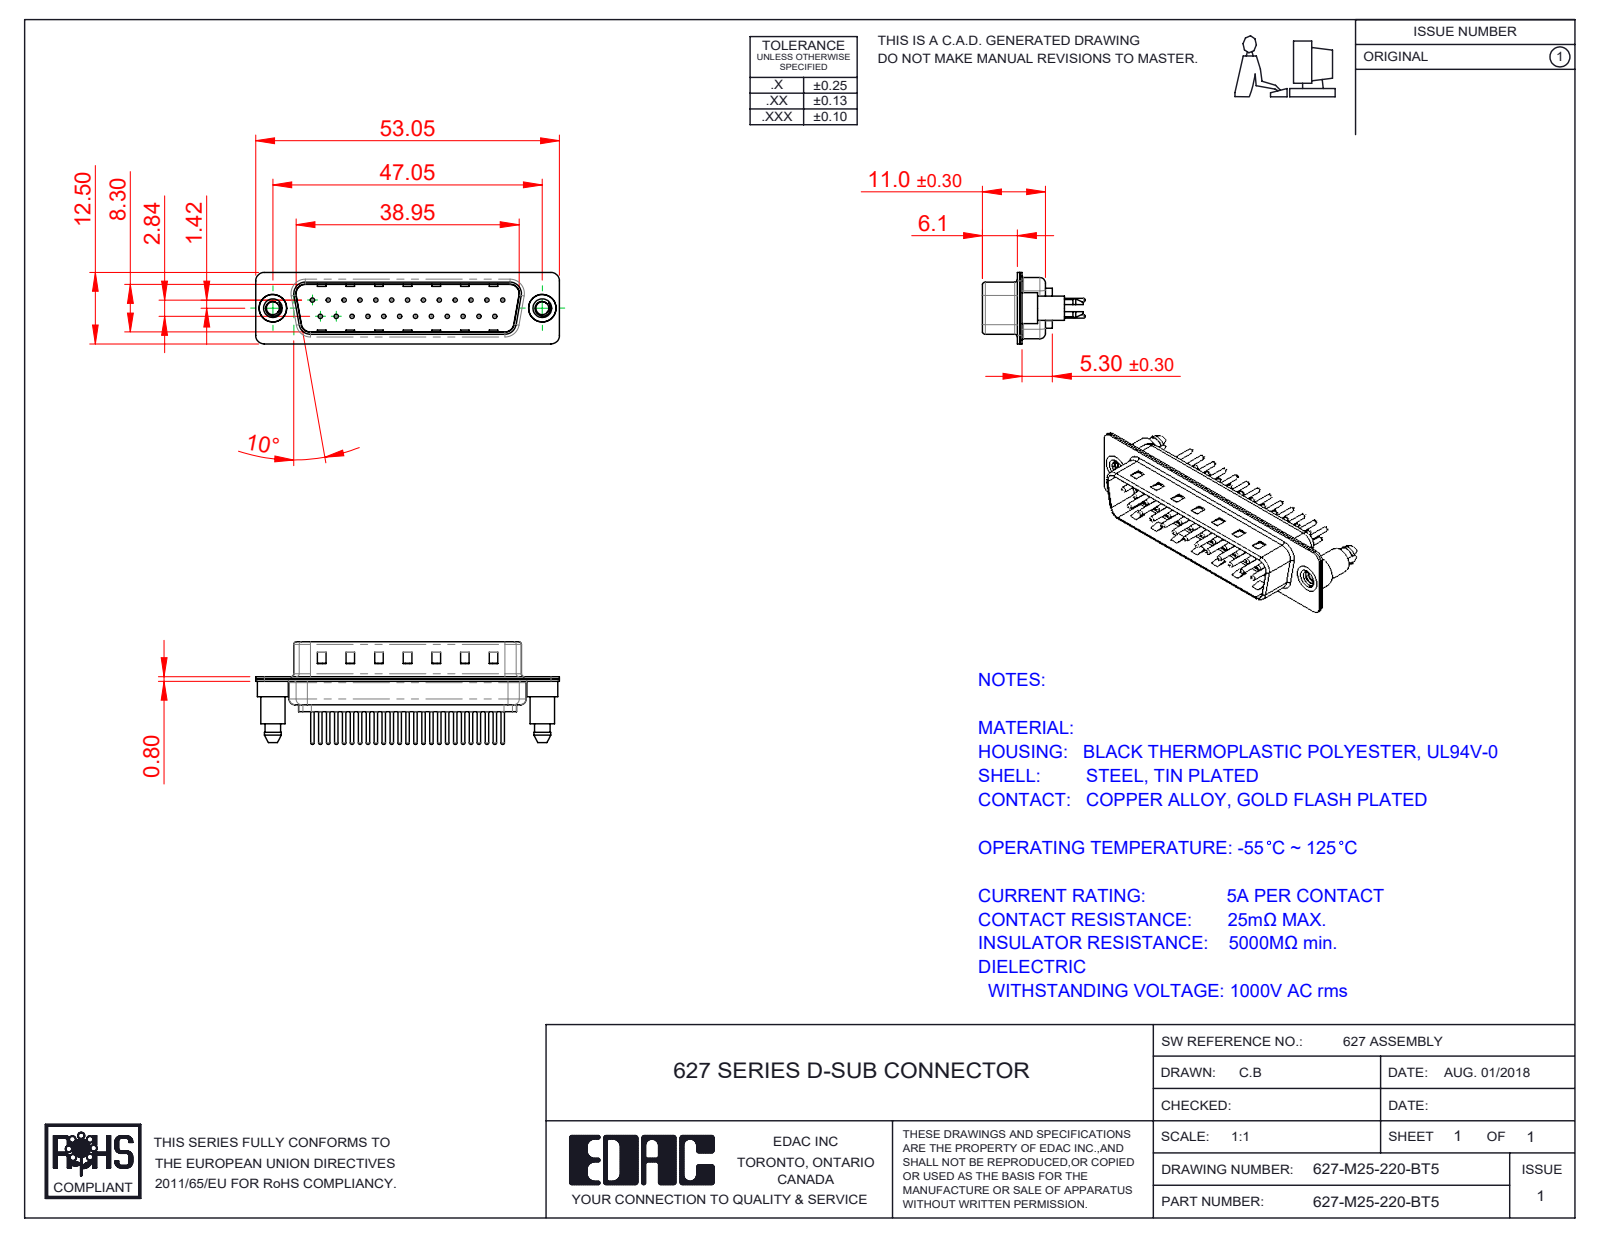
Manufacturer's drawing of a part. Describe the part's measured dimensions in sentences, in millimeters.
The part is named "627M Housing_25 Contacts; 627-M25-220-BT5; 627M Contact Row 2_20; 627M Shell Front_25 Contacts (+3 more)". Its 3-D file was written by "SolidWorks 2020 (CONFIG_CONTROL_DESIGN)". It is 30 solids with 1351 faces: 362 planar, 519 cylindrical and 470 other. Overall it measures 53.05 by 17.9 by 12.5 millimeters. Its volume is 2 853 cubic millimeters and its surface area 7 176 square millimeters. Round holes: 25 of diameter 0.75, 25 of diameter 1.6, 25 of diameter 2, 2 of diameter 2.26, 2 of diameter 4, 2 of diameter 4.8. Round bosses or shafts: 25 of diameter 1.5, 25 of diameter 0.6, 2 of diameter 5.4, 2 of diameter 4.9, 2 of diameter 4.25. Partial cylindrical surfaces (rounded edges, fillets, slot ends): 18 of radius 1.5, 12 of radius 2, 10 of radius 1.6, 8 of radius 0.5, 4 of radius 0.25, 4 of radius 0.6, 4 of radius 0.65, 4 of radius 0.9. The main face-to-face distances are 0.4, 0.8, 9.5, 9.1, 8.7, 9.9, 1.2, 6.1, 5.7, 0.75. The hole center spacings are 3.16, 2.77, 5.54, 8.31, 11.08, 13.85, 16.62, 5.03.
